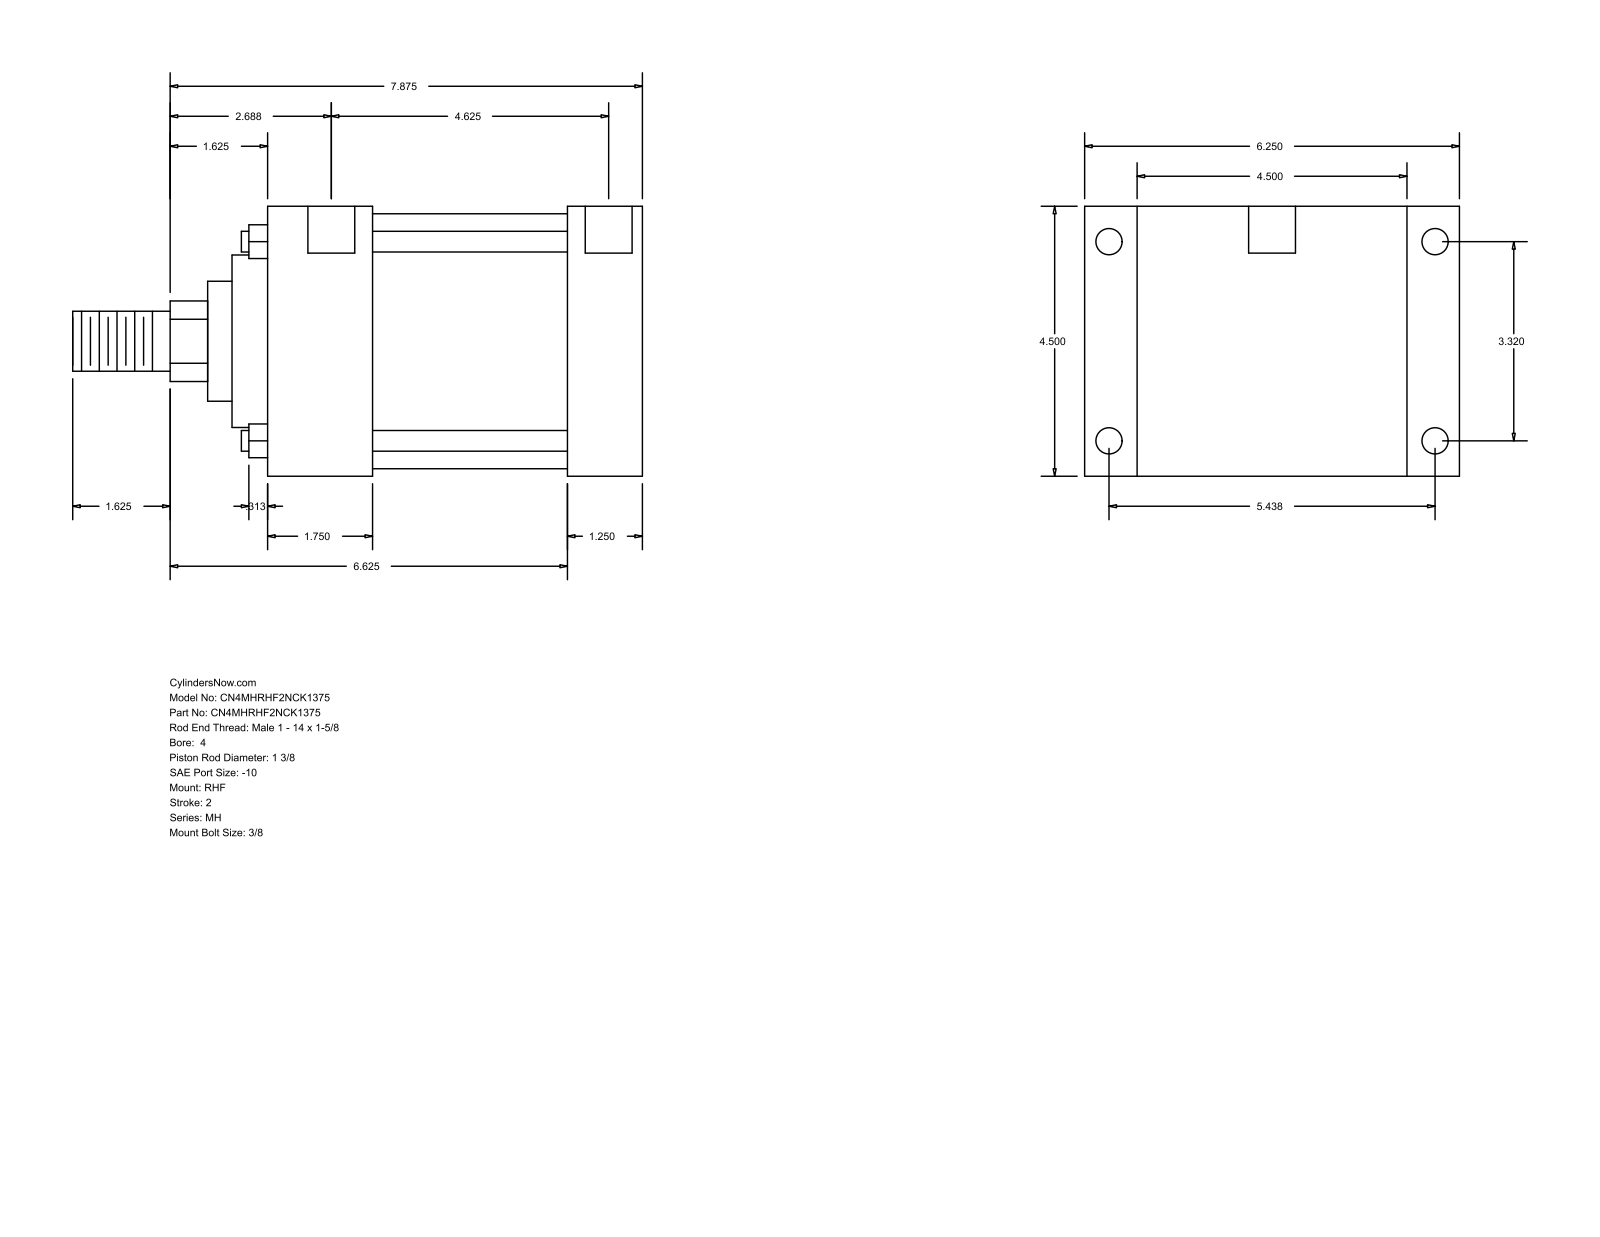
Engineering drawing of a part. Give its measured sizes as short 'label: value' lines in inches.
name: MH_RHF__0400_1.375
written by: GSSL Pune (CONFIG_CONTROL_DESIGN)
unit: in
bodies: 0 solids, 90 faces (61 planar, 29 cylindrical, 0 other)
size: 9.5 × 6.25 × 4.5
holes: 4× ⌀0.344, 4× ⌀0.438, 2× ⌀0.781
bosses: 4× ⌀0.345, 1× ⌀4.25, 1× ⌀2.875, 1× ⌀2, 1× ⌀1.375, 1× ⌀1
rounds: 1× R0.672
face distances: 4.5, 6.25, 1.25, 5, 0.875, 5.375, 1.75, 3.25, 4.5, 0.594
hole spacings: 3.32, 4.75, 5.438, 6.371, 0.062, 0.063, 4.625, 4.687
